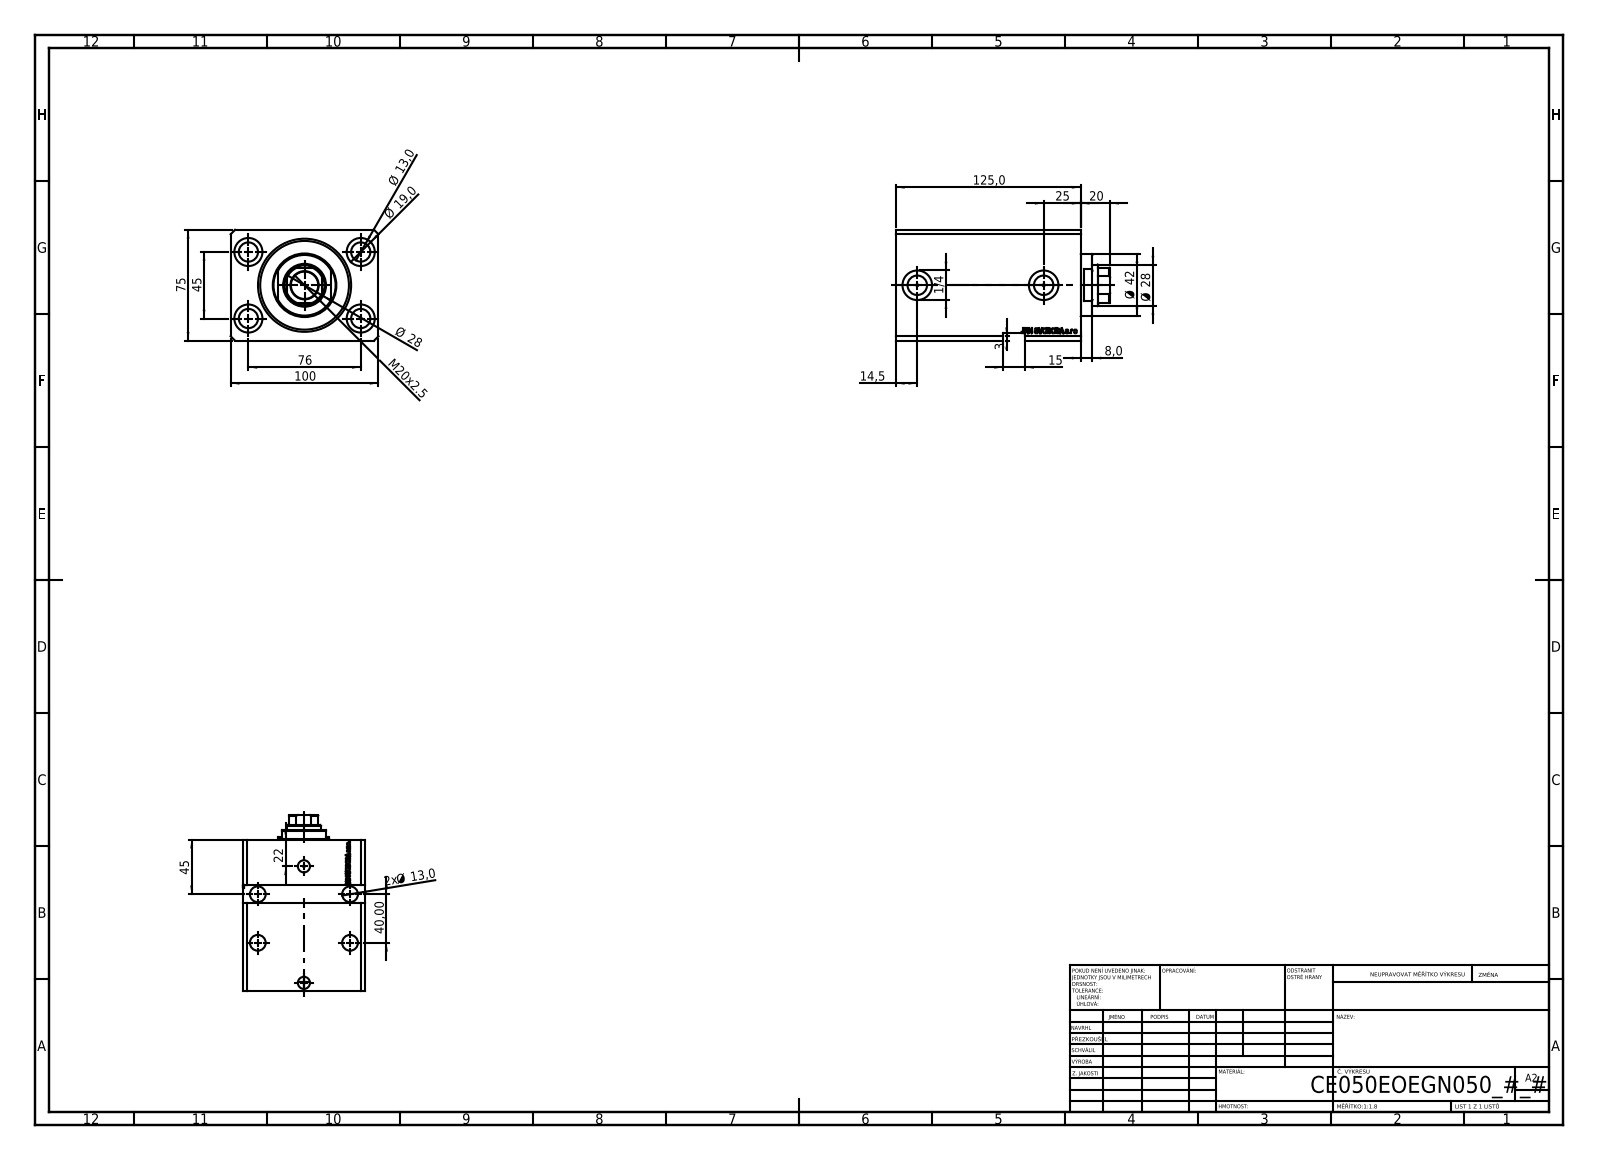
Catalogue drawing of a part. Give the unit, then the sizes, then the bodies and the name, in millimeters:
Units: millimetres
Overall size (bounding box): 145 × 100 × 75
Round holes (diameter × count): ⌀13 ×8, ⌀1.25 ×4, ⌀19 ×4, ⌀10 ×2, ⌀13.16 ×2, ⌀20 ×2, ⌀18.5 ×1, ⌀28 ×1, ⌀50 ×1, ⌀63 ×1
Round bosses / shafts (diameter × count): ⌀42 ×1
Partial cylindrical surfaces — rounded edges, fillets, slot ends (radius × count): R13.5 ×1
Main face-to-face distances: 75, 100, 125, 11.9, 113.1, 20, 105, 93.1, 70, 13
Hole centre spacings: 44.16, 76, 40, 44.42, 45, 49.98, 50.33, 73.57
Volume: 754 695 mm³ · Surface area: 138 585 mm²
Bodies: 3 solids, 938 faces (459 planar, 104 cylindrical, 375 other)
Part name (STEP PRODUCT): V250CE_C_VCP; V250CE_VC_E; V250CE_E_Body
STEP written by: SolidWorks 2019 (CONFIG_CONTROL_DESIGN)
